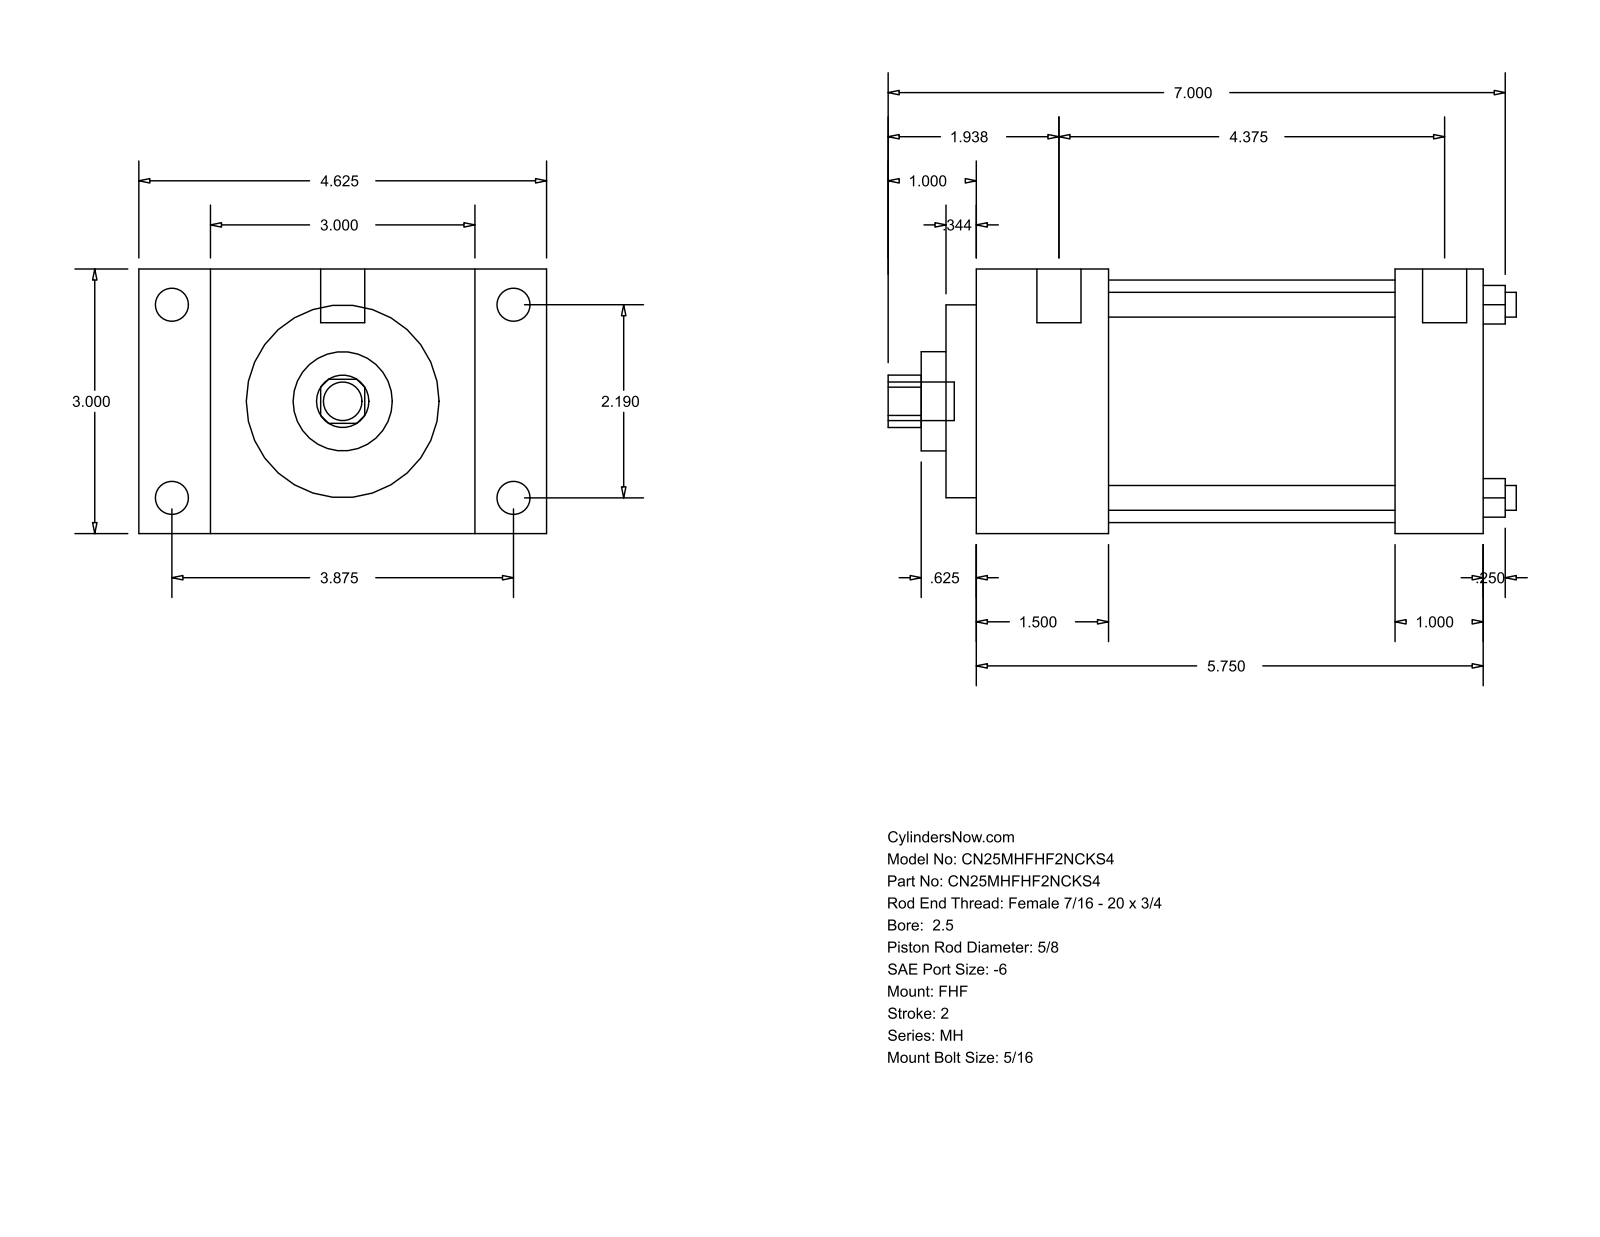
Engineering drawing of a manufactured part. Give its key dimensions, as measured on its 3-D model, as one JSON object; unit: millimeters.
{"part_name": "MH_FHF__0250_0.625", "step_written_by": "GSSL Pune (CONFIG_CONTROL_DESIGN)", "units": "millimeters", "bodies": {"solids": 0, "faces": 90, "planar": 61, "cylindrical": 29, "other": 0}, "overall_size": [180.97, 117.47, 76.2], "round_holes": [[7.14, 4], [15.88, 1], [28.57, 1], [55.55, 1], [69.85, 1]], "round_bosses_or_shafts": [[9.53, 4], [5.56, 4], [12.7, 2], [11.11, 1]], "partial_cylinders_radius": [[7.54, 1]], "face_to_face_distances": [76.2, 146.05, 38.1, 107.95, 20.64, 96.84, 117.48, 25.4, 120.65, 82.55], "hole_center_spacings": [39.33, 55.62, 78.66]}
